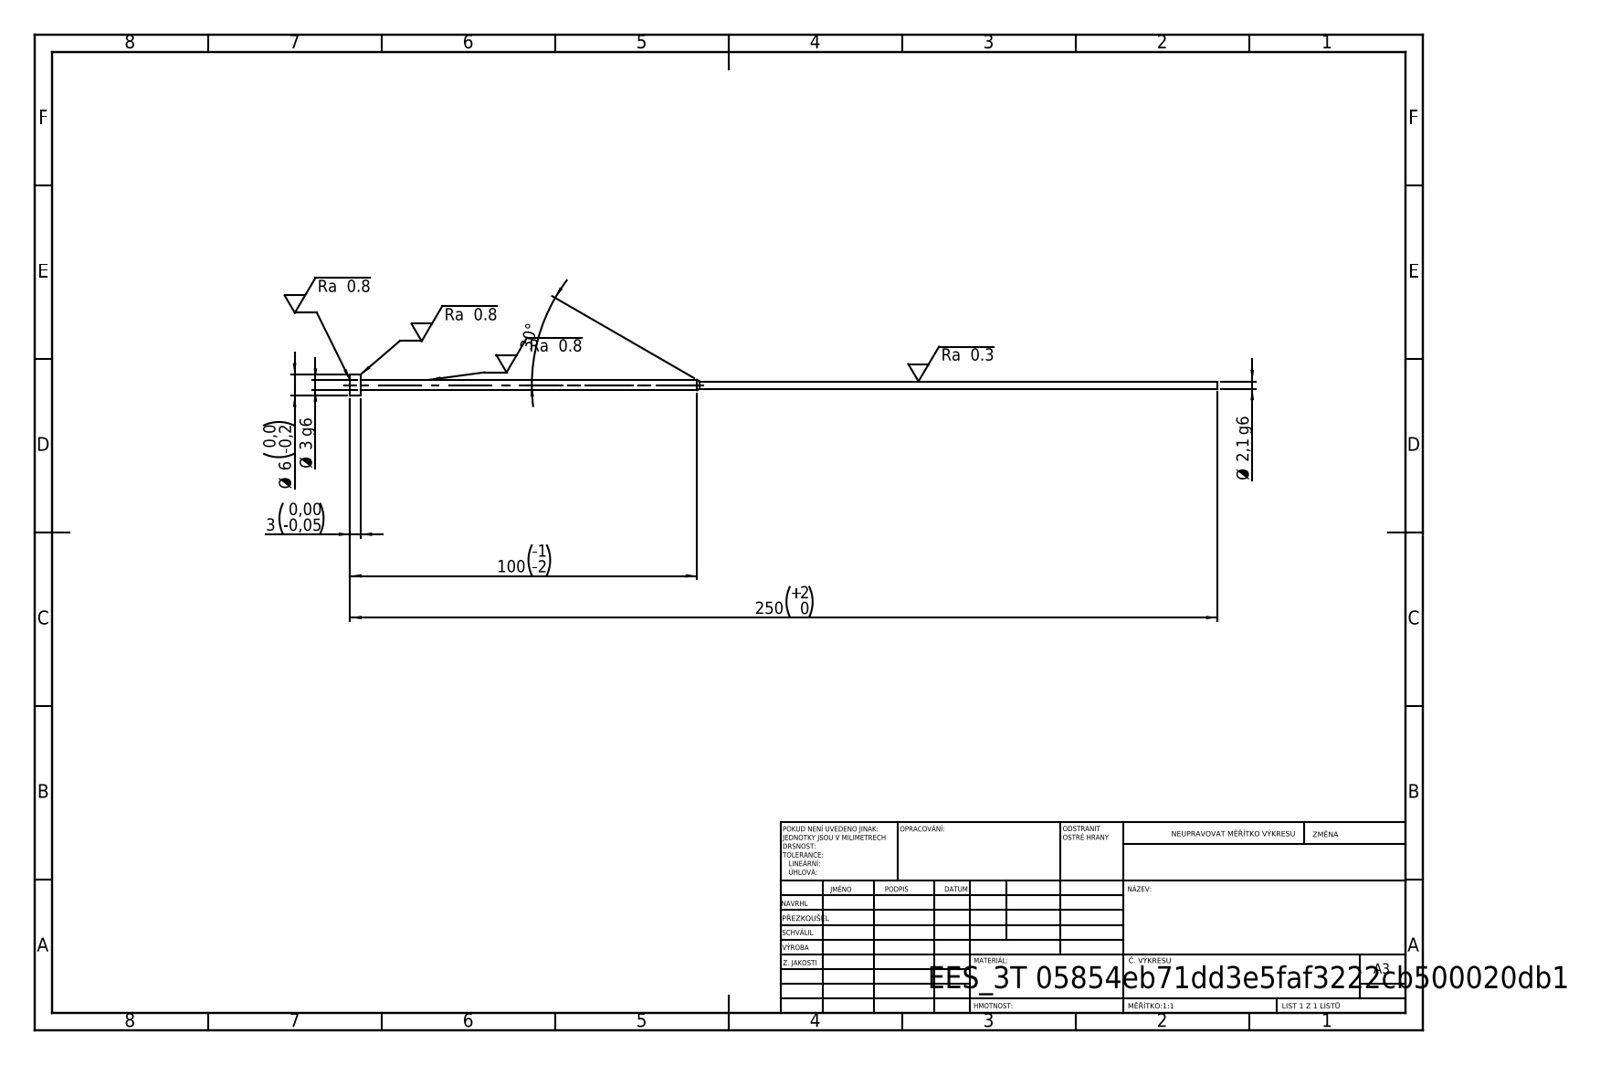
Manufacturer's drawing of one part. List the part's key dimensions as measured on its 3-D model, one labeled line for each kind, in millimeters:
STEP written by: SolidWorks 2019 (CONFIG_CONTROL_DESIGN)
Units: millimetres
Bodies: 1 solid, 11 faces (3 planar, 6 cylindrical, 2 other)
Overall size (bounding box): 250 × 6 × 6
Volume: 1 291 mm³ · Surface area: 2 015 mm²
Round bosses / shafts (diameter × count): ⌀6 ×1, ⌀3 ×1, ⌀2.1 ×1
Main face-to-face distances: 3, 247, 250
